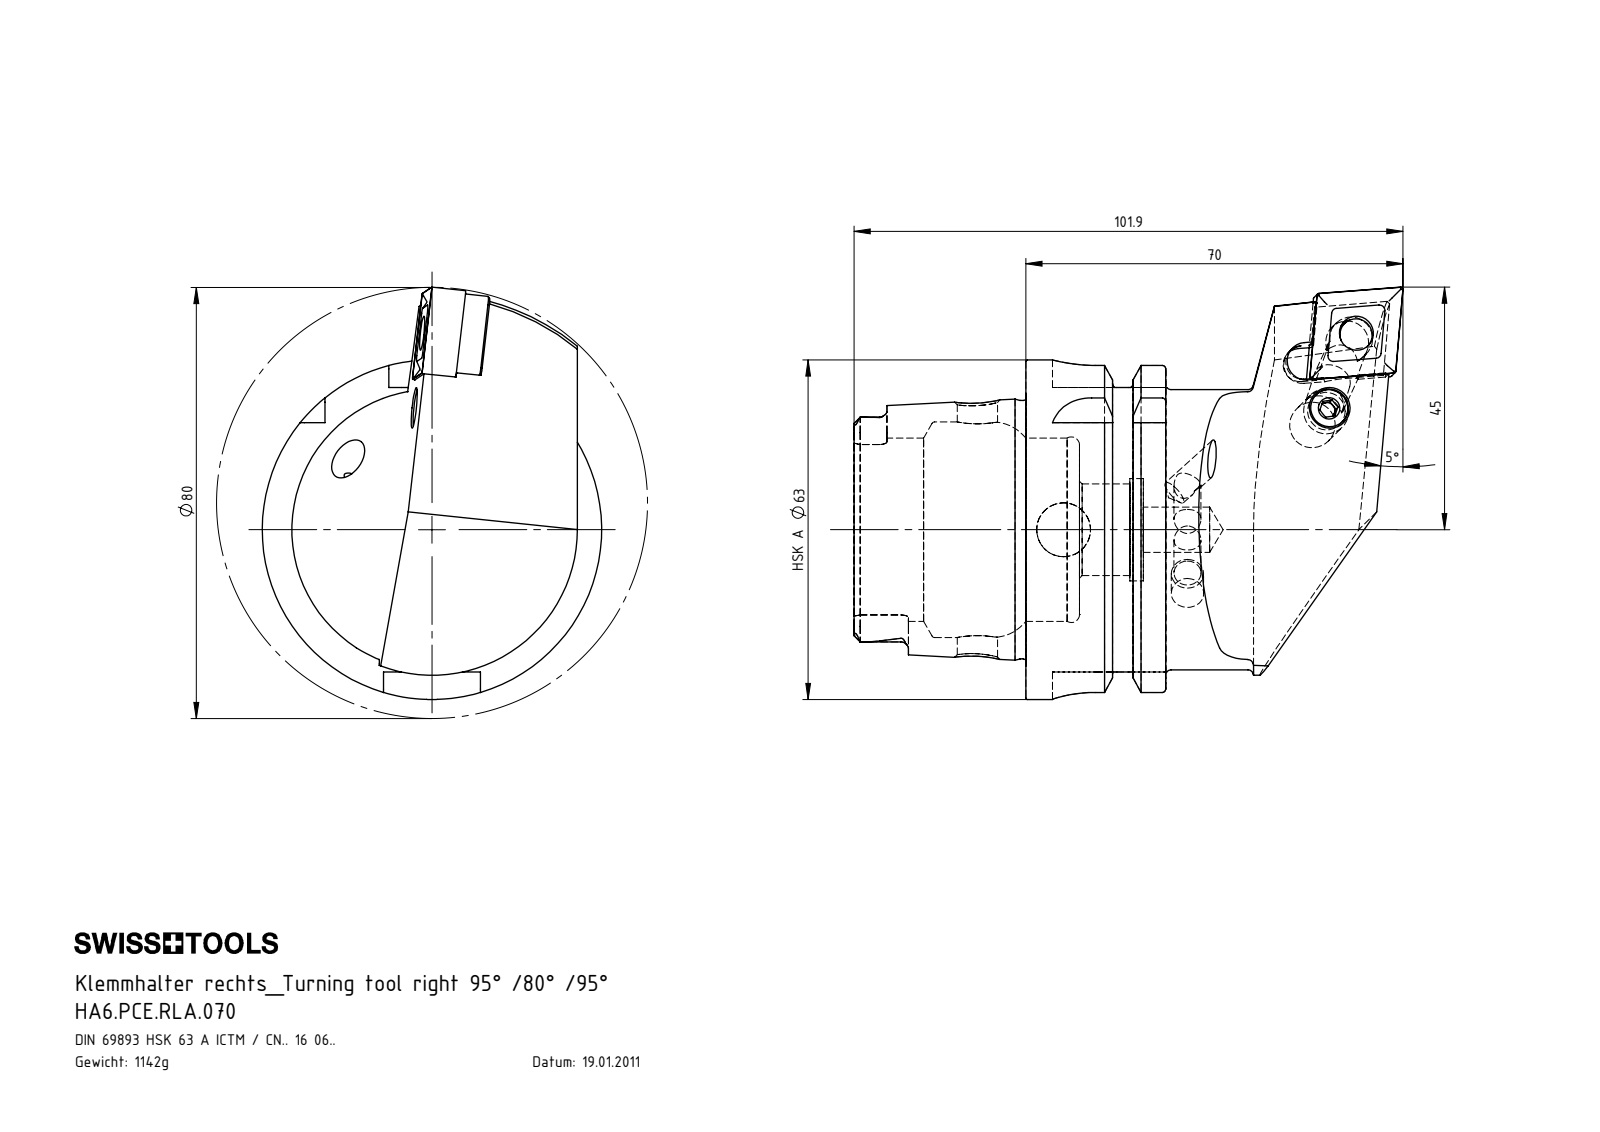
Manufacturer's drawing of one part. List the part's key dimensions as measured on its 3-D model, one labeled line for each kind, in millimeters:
Part name (STEP PRODUCT): HA6-PCE.RLA.070; KVT_MB_600_060; WCE; WCE-ER3.101.000_A (+4 more)
STEP written by: SolidWorks 2012 (CONFIG_CONTROL_DESIGN)
Units: millimetres
Bodies: 7 solids, 367 faces (118 planar, 101 cylindrical, 148 other)
Overall size (bounding box): 101.9 × 76.5 × 63
Volume: 144 958 mm³ · Surface area: 34 121 mm²
Round holes (diameter × count): ⌀5 ×2, ⌀8.4 ×2, ⌀6.35 ×1, ⌀7 ×1, ⌀7.5 ×1, ⌀8.05 ×1, ⌀10 ×1, ⌀17 ×1, ⌀19 ×1, ⌀34 ×1, ⌀40 ×1
Round bosses / shafts (diameter × count): ⌀6 ×2, ⌀63 ×1, ⌀54.95 ×1, ⌀52 ×1, ⌀47.94 ×1, ⌀8 ×1, ⌀7.9 ×1, ⌀6.4 ×1
Partial cylindrical surfaces — rounded edges, fillets, slot ends (radius × count): R1.4 ×6, R0.4 ×4, R1.5 ×4, R8 ×4, R3.5 ×3, R2.82 ×2, R2.88 ×2, R3.1 ×1
Main face-to-face distances: 25.95, 16, 9.95, 31.9, 41.85, 57.85, 52.8, 21.8, 4.76, 11.85
Hole centre spacings: 14.76, 14.99
